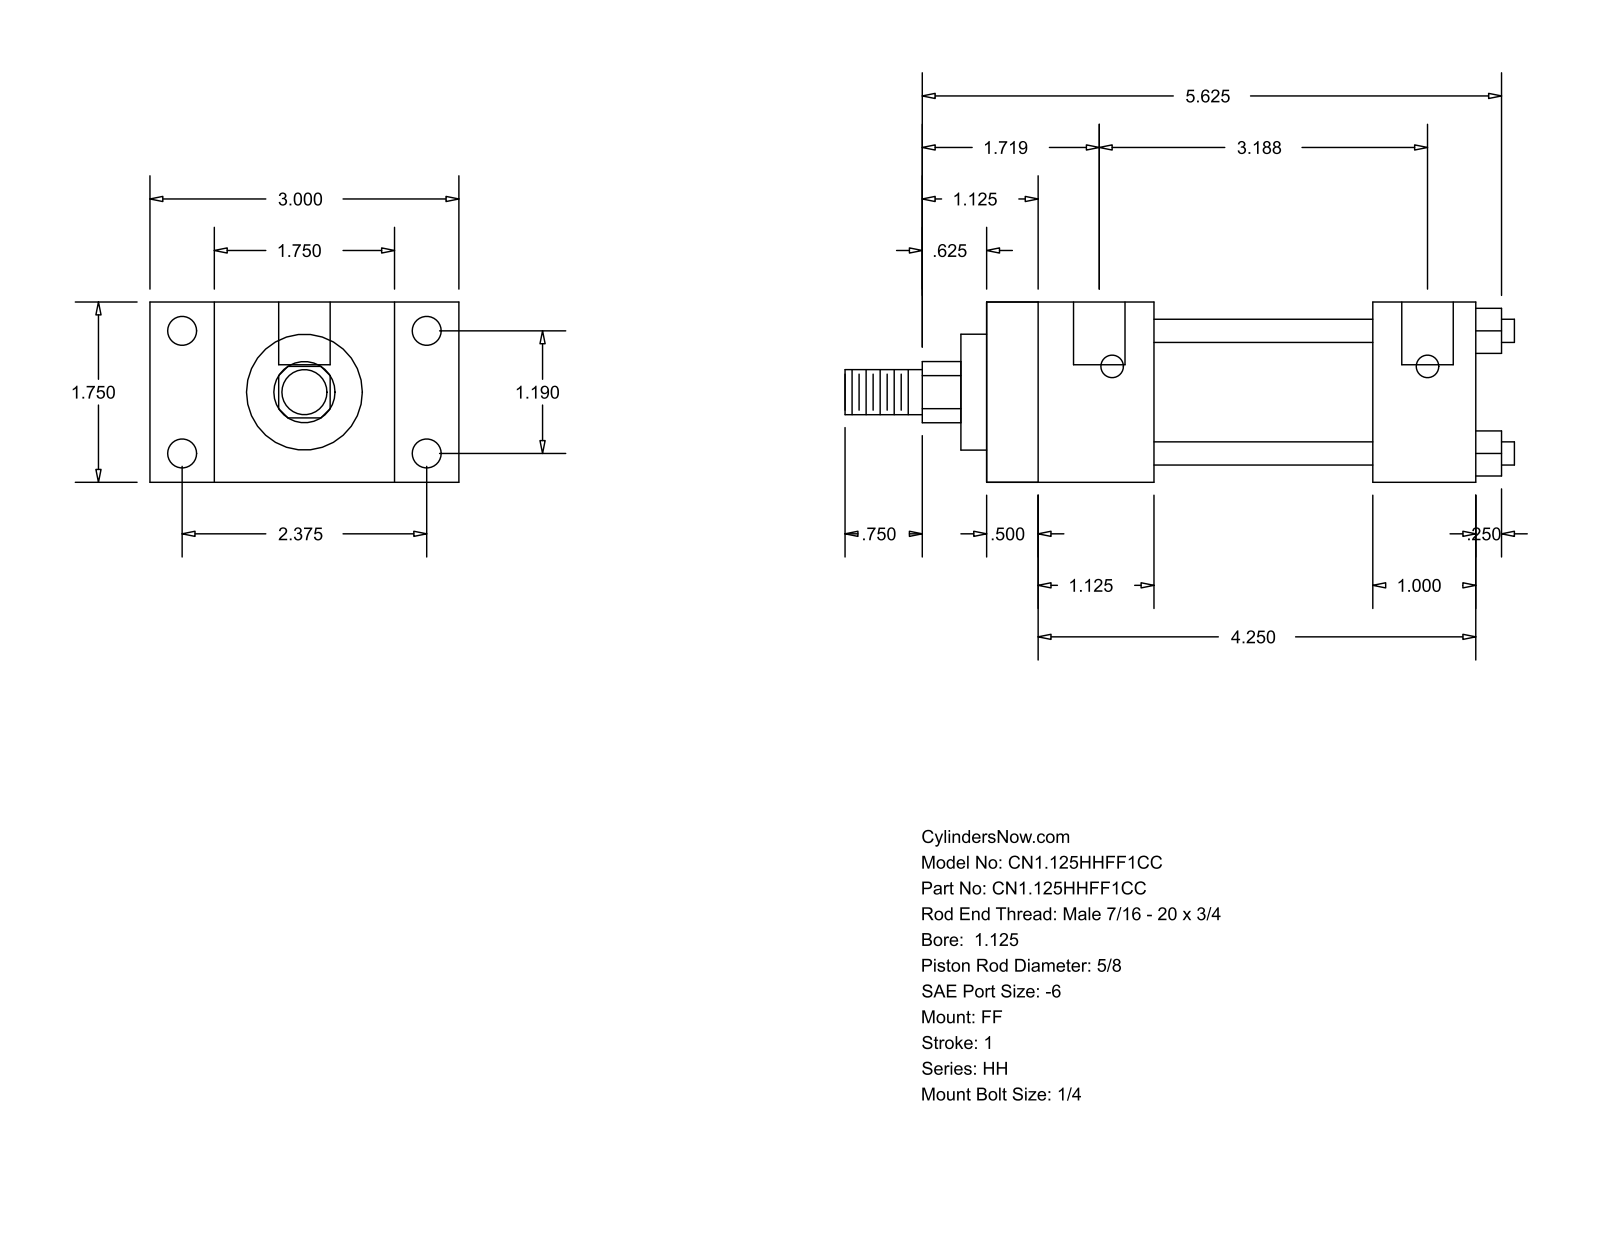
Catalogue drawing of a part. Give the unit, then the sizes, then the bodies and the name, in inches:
Units: inches
Overall size (bounding box): 6.5 × 3 × 1.75
Round holes (diameter × count): ⌀0.219 ×4, ⌀0.281 ×4, ⌀0.5 ×2
Round bosses / shafts (diameter × count): ⌀0.225 ×4, ⌀1.375 ×1, ⌀1.125 ×1, ⌀0.625 ×1, ⌀0.437 ×1
Partial cylindrical surfaces — rounded edges, fillets, slot ends (radius × count): R0.297 ×1
Main face-to-face distances: 1.75, 4.75, 0.5, 4.25, 0.625, 1.125, 2.375, 1.625, 3.75, 3.25
Hole centre spacings: 1.19, 2.375, 2.656, 3.063, 0.125, 3.187
Bodies: 0 solids, 92 faces (64 planar, 28 cylindrical, 0 other)
Part name (STEP PRODUCT): HH_FF__0112_0.625
STEP written by: GSSL Pune (CONFIG_CONTROL_DESIGN)
